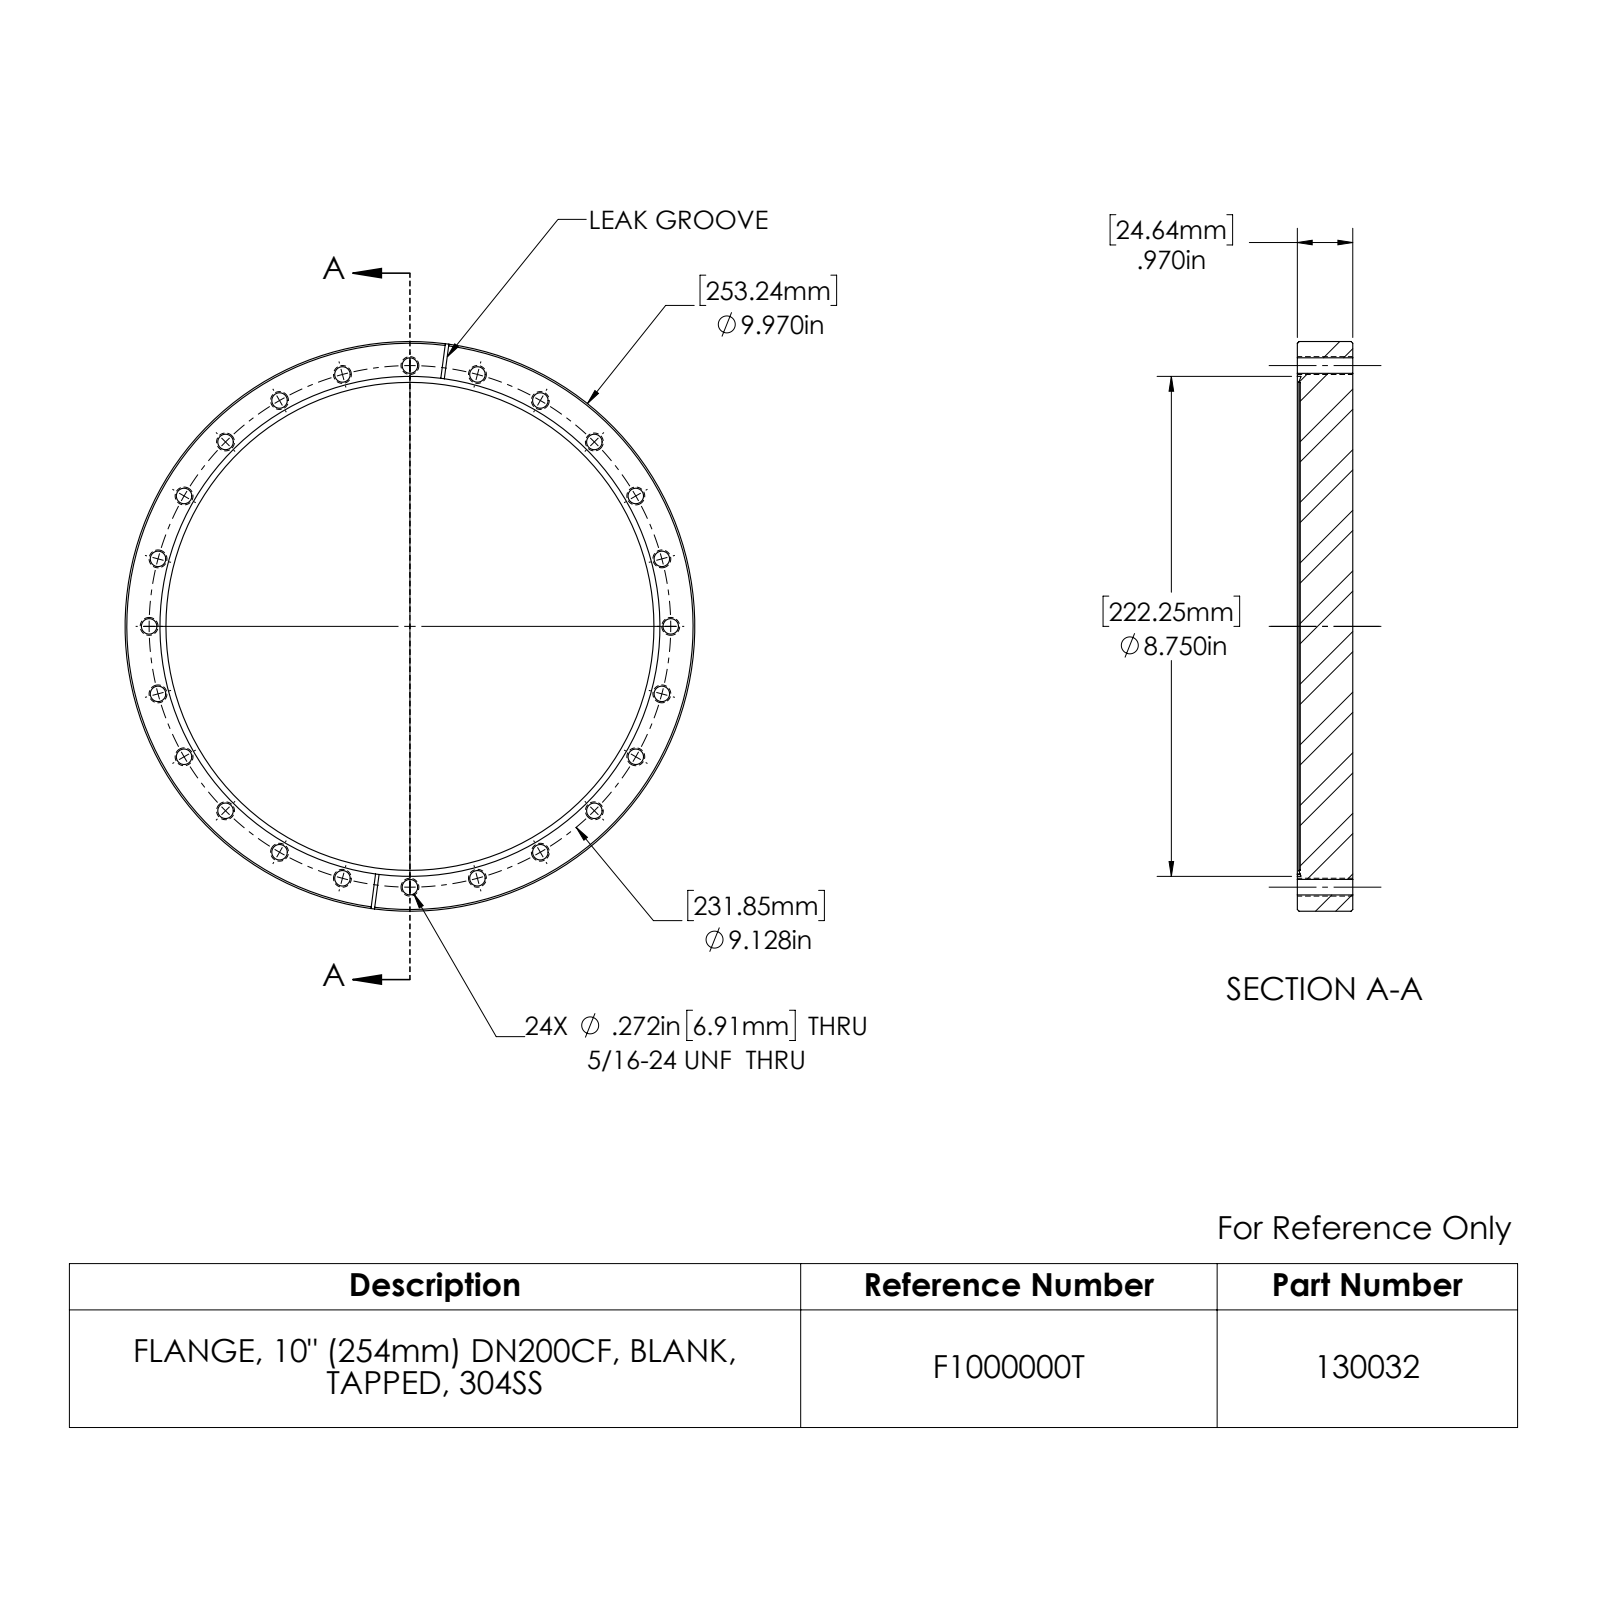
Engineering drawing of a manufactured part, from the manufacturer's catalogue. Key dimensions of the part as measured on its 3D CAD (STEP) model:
Part name (STEP PRODUCT): 130032_C
STEP written by: SolidWorks 2022 (CONFIG_CONTROL_DESIGN)
Units: inches
Bodies: 1 solid, 77 faces (8 planar, 56 cylindrical, 13 other)
Overall size (bounding box): 9.97 × 9.97 × 0.97
Volume: 71.29 in³ · Surface area: 205.1 in²
Round holes (diameter × count): ⌀0.272 ×24, ⌀8.54 ×1, ⌀8.75 ×1
Round bosses / shafts (diameter × count): ⌀9.97 ×1
Partial cylindrical surfaces — rounded edges, fillets, slot ends (radius × count): R1.25 ×2
Main face-to-face distances: 0.919, 0.051, 0.97, 0.062, 0.067, 0.057
Hole centre spacings: 4.564, 8.433, 2.363, 4.564, 7.905, 1.191, 3.493, 5.557
